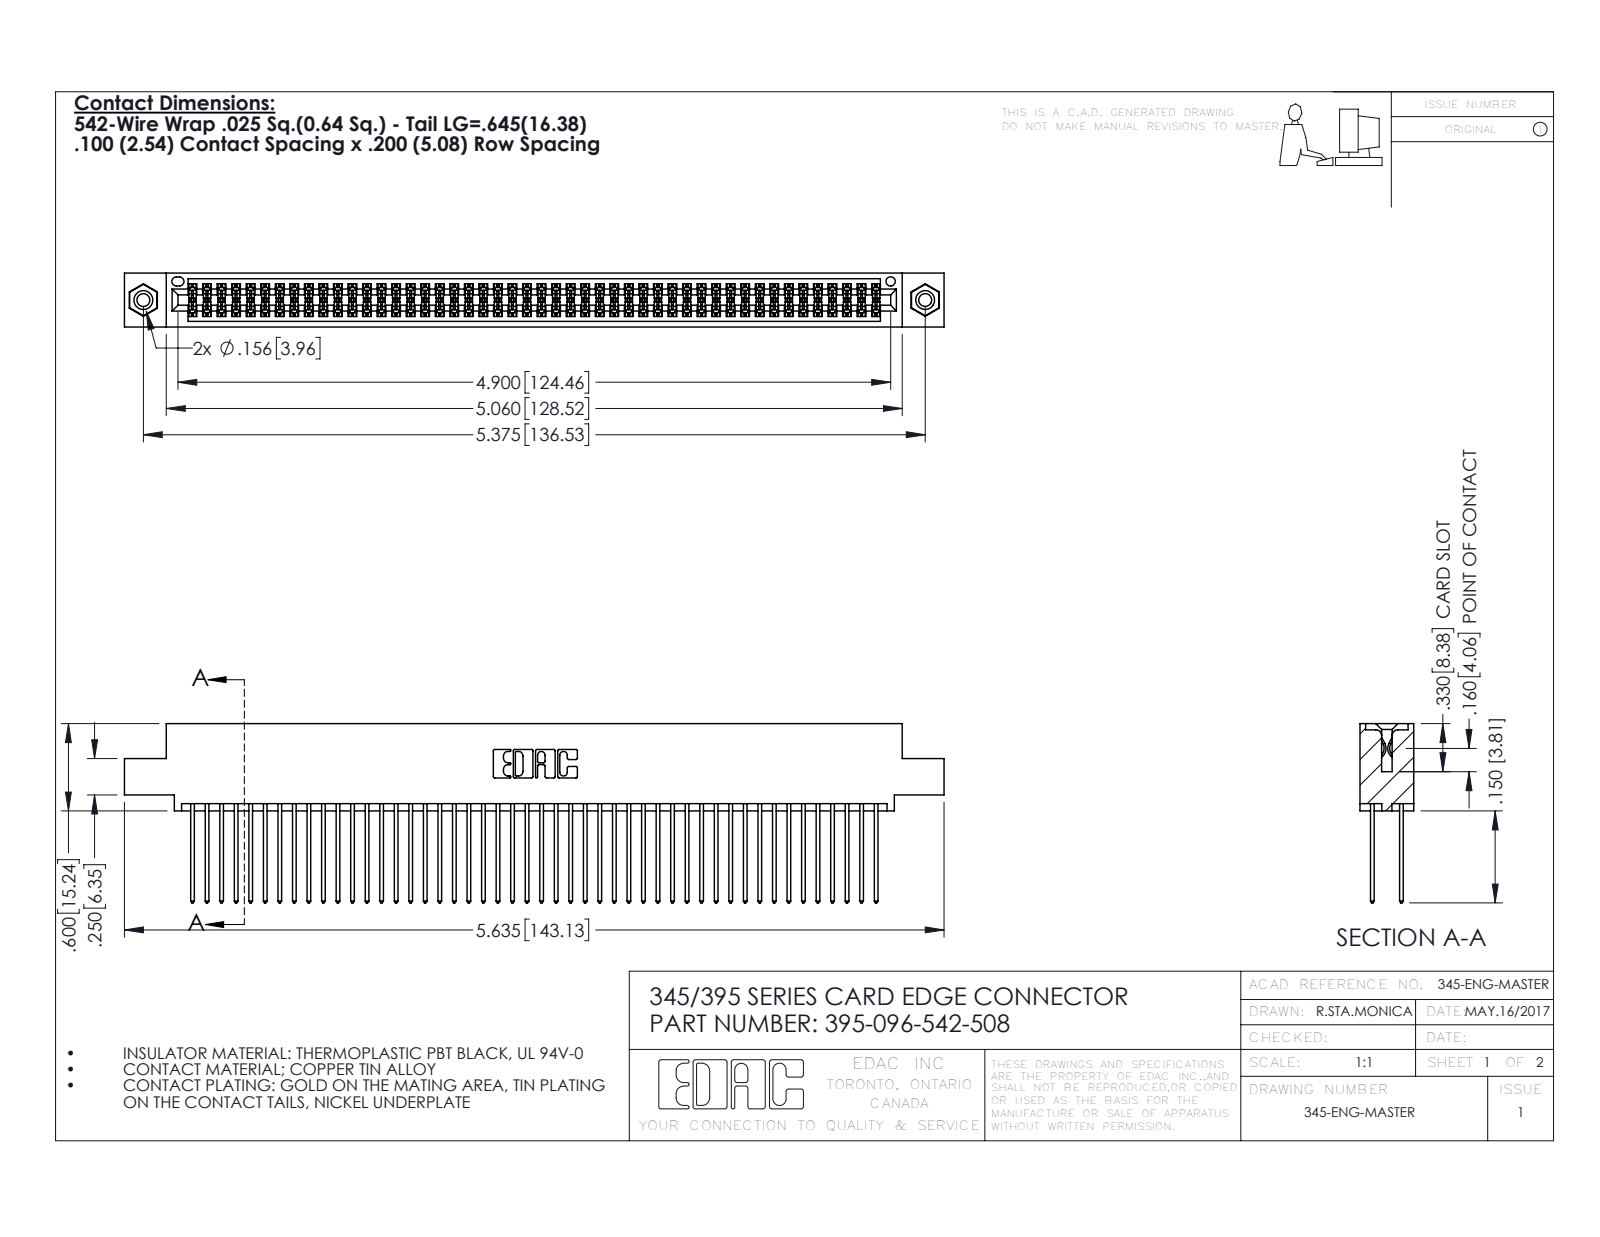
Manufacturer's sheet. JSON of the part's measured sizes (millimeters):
{"part_name": "395-096-542-508; 345-292-001_345-293-142; 345 Part_0.110 Offset - 0.156 Dia-TI; 345-250-001_345-250-003-102", "step_written_by": "SolidWorks 2016 (CONFIG_CONTROL_DESIGN)", "units": "millimeters", "bodies": {"solids": 99, "faces": 4990, "planar": 3284, "cylindrical": 1690, "other": 16}, "overall_size": [143.1, 31.3, 9.4], "volume_mm3": 14300, "surface_area_mm2": 23490, "round_holes": [[2.3, 2], [3.2, 2], [4, 2], [1.6, 1]], "round_bosses_or_shafts": [[3.9, 2]], "partial_cylinders_radius": [[0.2, 144], [0.3, 96], [0.3, 22], [0.2, 6], [0.8, 6], [0.7, 3], [0.4, 2], [0.5, 2]], "face_to_face_distances": [1.8, 7.6, 5.1, 2.5, 6.9, 0.6, 5.7, 9.4, 4.4, 3.8], "hole_center_spacings": [6.9, 130.5, 136.5]}
